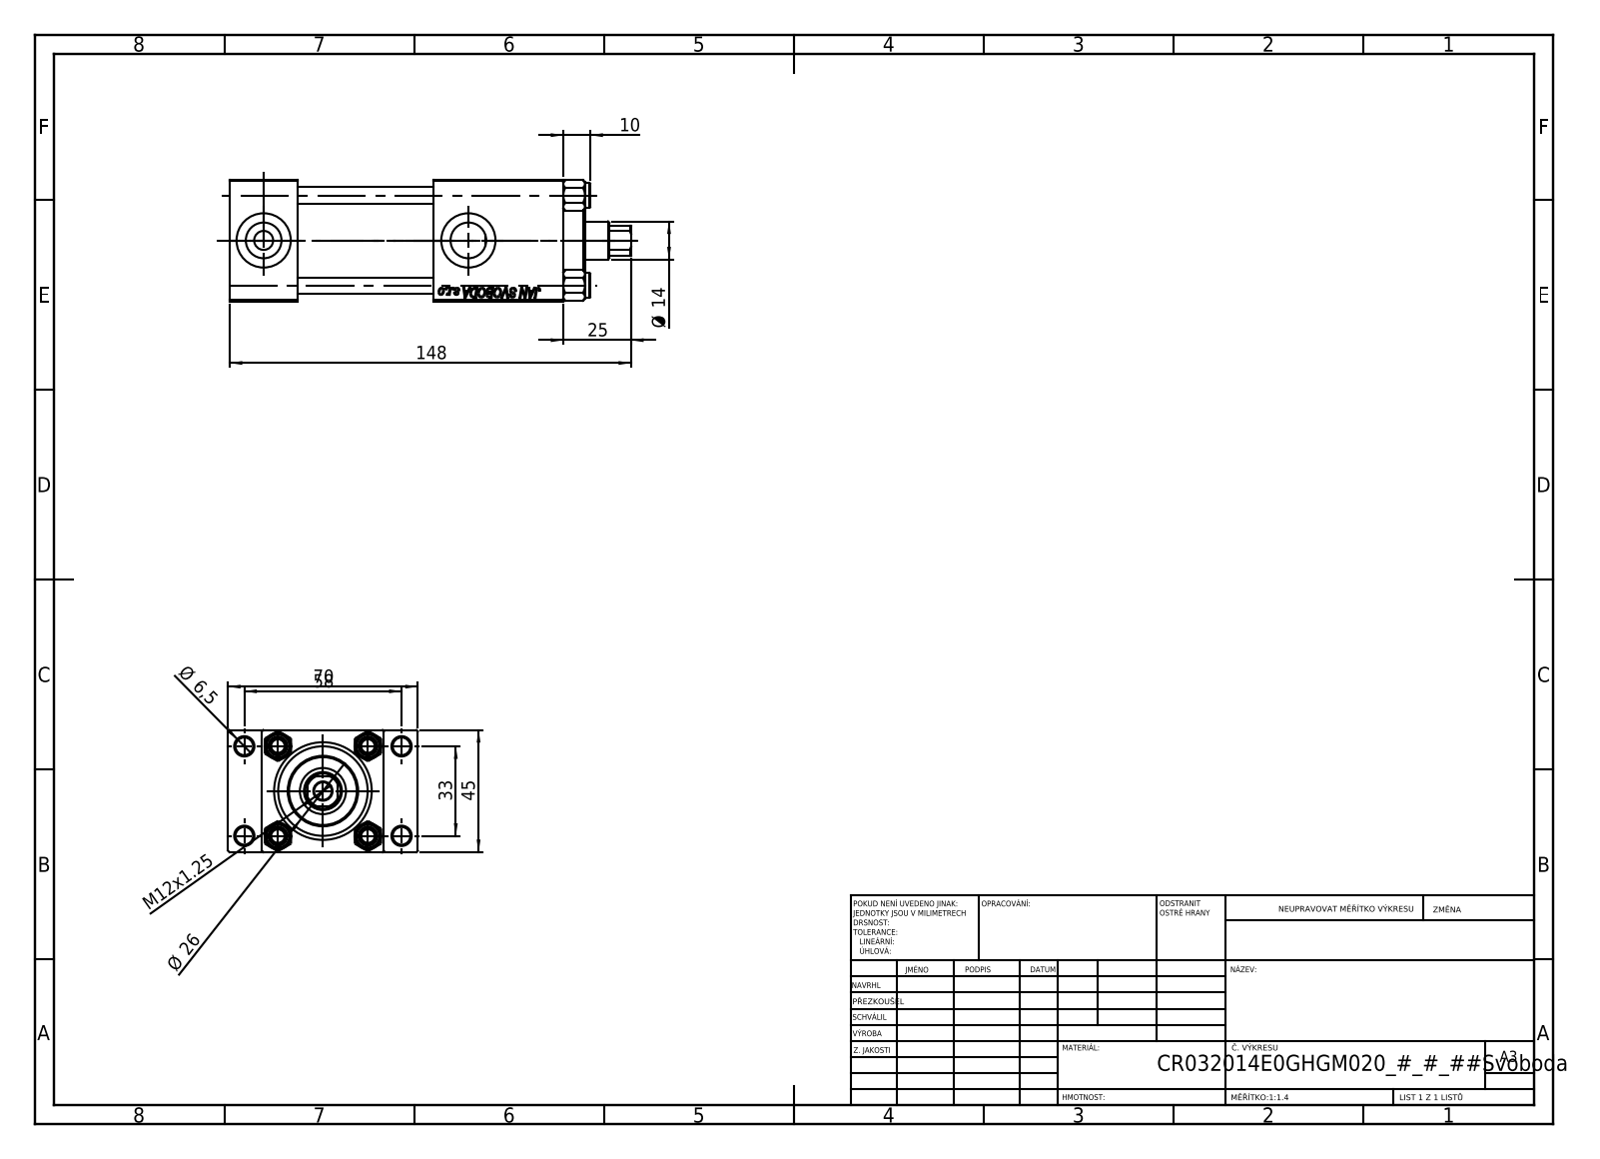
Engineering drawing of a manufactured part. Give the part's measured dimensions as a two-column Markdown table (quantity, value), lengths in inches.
| quantity | value |
| --- | --- |
| part name | V215CR_TYCINKA_E; V215_VC_A; NUT_M5_E; V215CR_E_Body (+1 more) |
| STEP written by | SolidWorks 2019 (CONFIG_CONTROL_DESIGN) |
| units | inches |
| bodies | 11 solids, 1135 faces (497 planar, 86 cylindrical, 552 other) |
| overall size | 5.827 × 2.756 × 1.772 |
| volume | 13.41 in³ |
| surface area | 118.3 in² |
| round holes (diameter × count) | 0.256 × 5, 0.236 × 4, 0.276 × 2, 0.518 × 2, 0.787 × 2, 0.551 × 1, 0.669 × 1, 0.945 × 1, 1.26 × 1, 1.299 × 1 |
| round bosses / shafts (diameter × count) | 0.354 × 4, 1.496 × 1, 1.024 × 1 |
| partial cylindrical surfaces (radius × count) | 0.256 × 1 |
| main face-to-face distances | 1.772, 0.984, 0.492, 2.264, 4.843, 3.858, 1.969, 2.953, 1.89, 3.713 |
| hole center spacings | 0.488, 0.924, 1.307, 1.314, 1.392, 1.795, 2.219, 1.299 |
